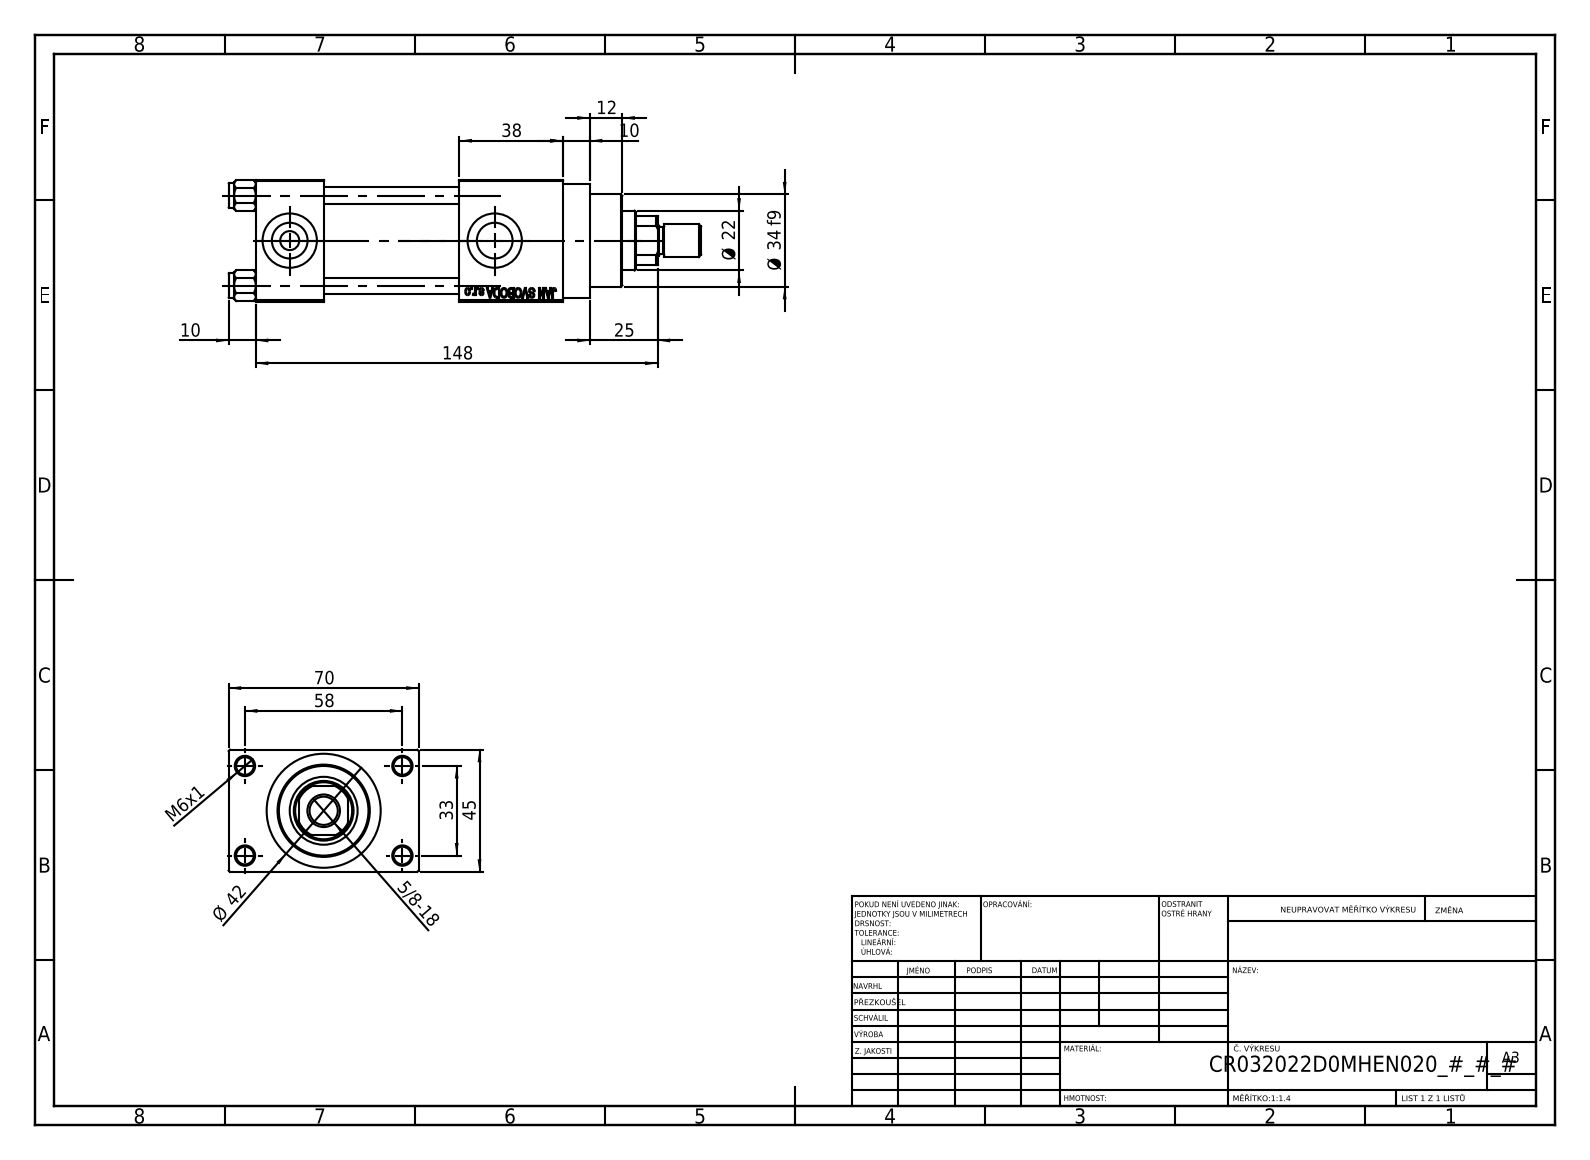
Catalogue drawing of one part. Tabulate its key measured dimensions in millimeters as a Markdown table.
| quantity | value |
| --- | --- |
| part name | NUT_M5_D; V215CR_D_TYCINKA; V215CR_D_Body; V215CR_VCP_D (+2 more) |
| STEP written by | SolidWorks 2019 (CONFIG_CONTROL_DESIGN) |
| units | millimeters |
| bodies | 12 solids, 1116 faces (500 planar, 92 cylindrical, 524 other) |
| overall size | 174 × 70 × 45 |
| volume | 244 722 mm³ |
| surface area | 80 821 mm² |
| round holes (diameter × count) | 6 × 4, 6.5 × 4, 7 × 2, 13.16 × 2, 20 × 2, 10.5 × 1, 22 × 1, 24 × 1, 25 × 1, 32 × 1, 33 × 1 |
| round bosses / shafts (diameter × count) | 9 × 4, 42 × 1, 38 × 1, 34 × 1, 12 × 1, 10 × 1 |
| partial cylindrical surfaces (radius × count) | 10.5 × 1 |
| main face-to-face distances | 45, 25, 50, 12.5, 75, 57.5, 88, 38, 113, 70 |
| hole center spacings | 12.4, 23.48, 33.2, 33.37, 35.35, 45.6, 56.35, 33 |
